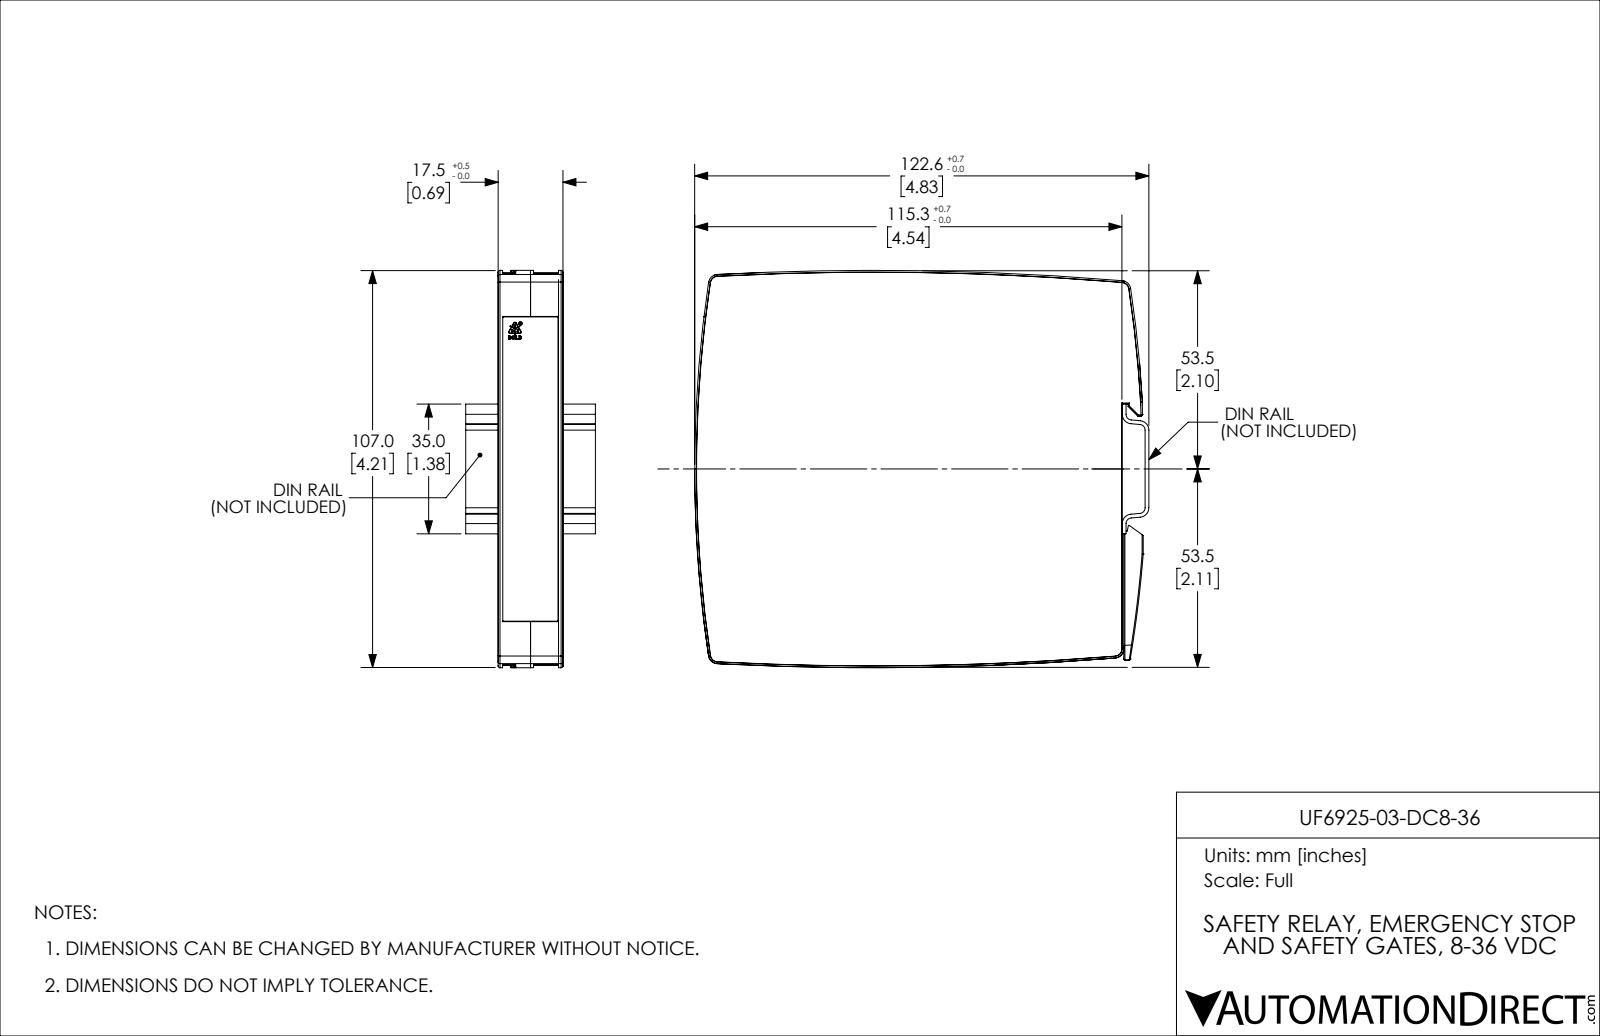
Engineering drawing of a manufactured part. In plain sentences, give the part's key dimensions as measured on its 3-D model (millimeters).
The part is named "00_UF6925". Its 3-D file was written by "SolidWorks 2018 (AUTOMOTIVE_DESIGN)". It is 14 solids with 660 faces: 394 planar, 87 cylindrical and 179 other. Overall it measures 121.1 by 107.2 by 17.8 millimeters. Its volume is 46 670 cubic millimeters and its surface area 66 710 square millimeters. Round holes: 1 of diameter 0.9. Round bosses or shafts: 1 of diameter 0.9. Partial cylindrical surfaces (rounded edges, fillets, slot ends): 8 of radius 0.1, 4 of radius 0.8, 3 of radius 0.4, 2 of radius 0.2, 2 of radius 0.4, 2 of radius 0.4, 2 of radius 803.8, 2 of radius 804.6. The main face-to-face distances are 1.2, 16.4, 15.1, 1.3, 16.5, 17.7, 17.6, 17.8, 8.9, 8.8.
